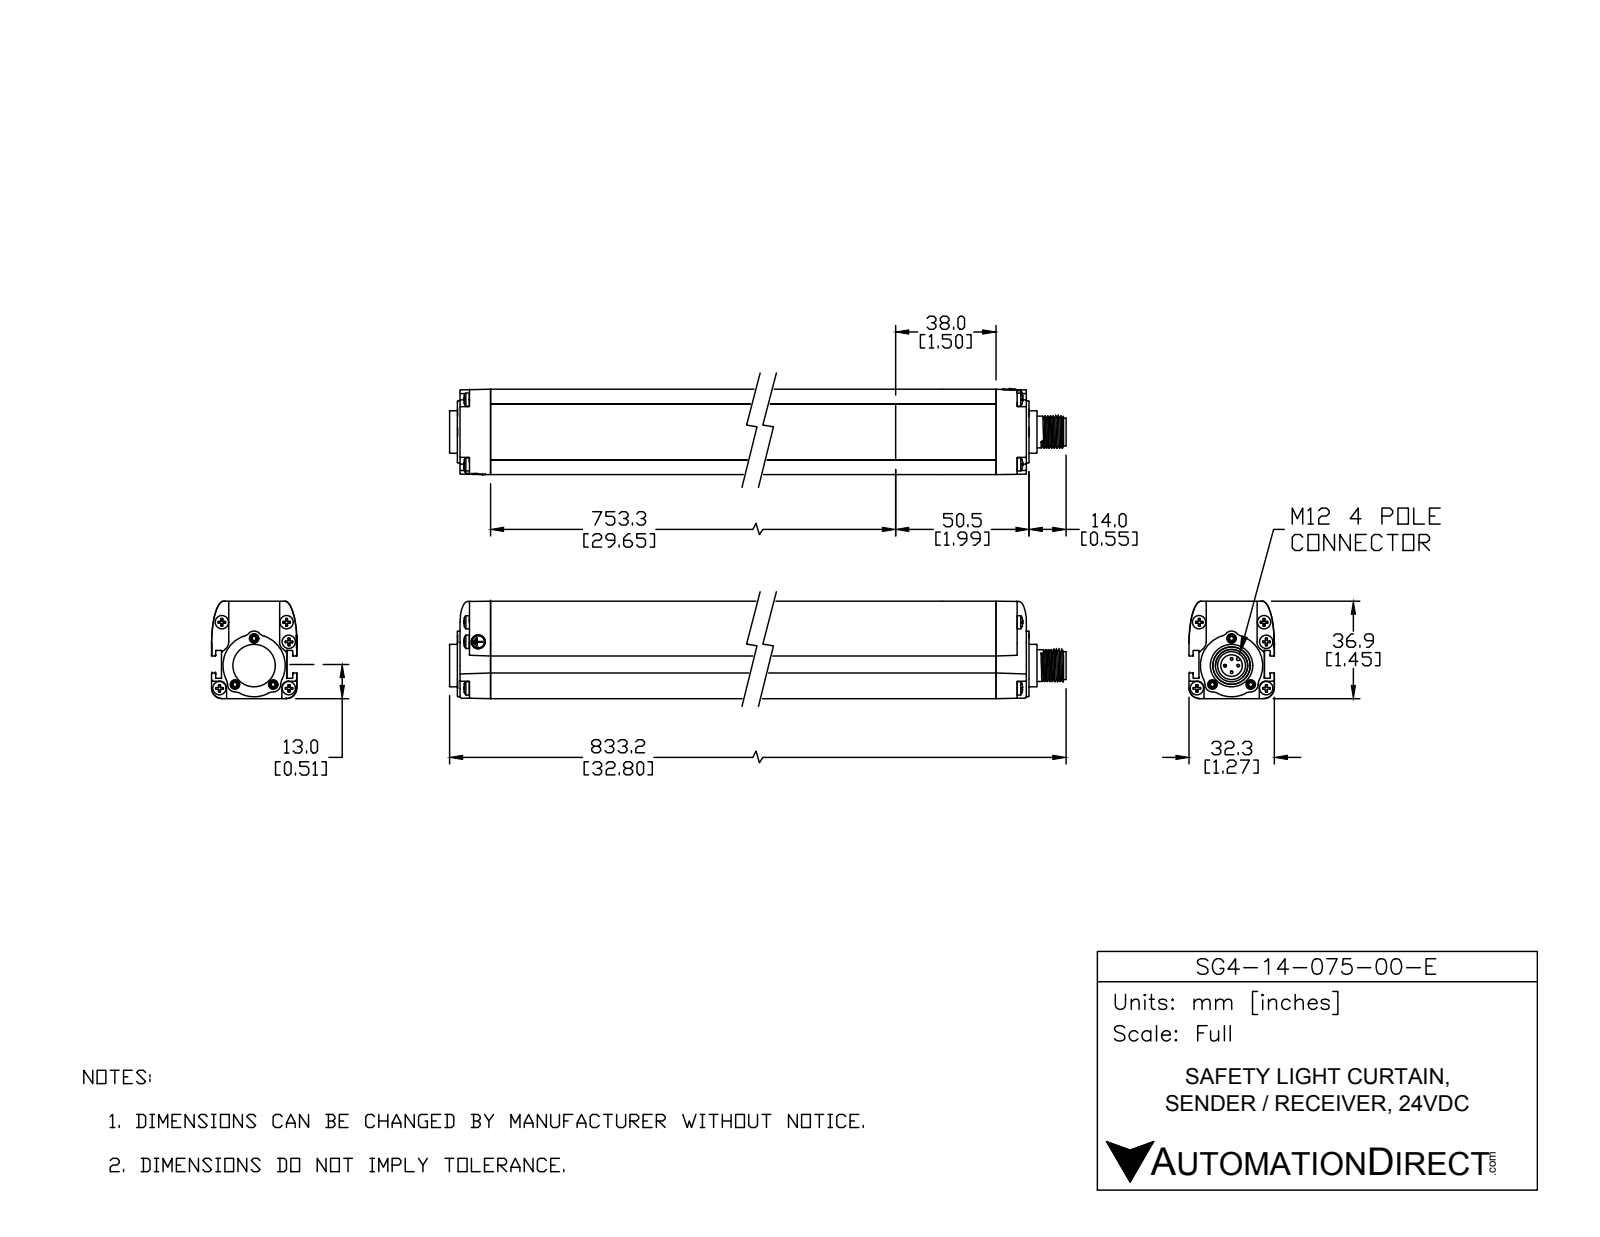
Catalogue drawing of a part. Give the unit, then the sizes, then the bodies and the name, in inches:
Units: inches
Overall size (bounding box): 32.805 × 2.48 × 2.055
Round holes (diameter × count): ⌀0.106 ×6, ⌀0.209 ×6, ⌀0.081 ×4, ⌀0.165 ×4, ⌀0.26 ×4, ⌀0.059 ×3, ⌀0.142 ×3, ⌀0.323 ×1, ⌀0.376 ×1, ⌀0.433 ×1, ⌀0.563 ×1
Round bosses / shafts (diameter × count): ⌀0.197 ×10, ⌀0.394 ×4, ⌀0.039 ×4, ⌀0.185 ×2, ⌀0.63 ×1, ⌀0.55 ×1, ⌀0.472 ×1, ⌀0.413 ×1
Partial cylindrical surfaces — rounded edges, fillets, slot ends (radius × count): R0.008 ×148, R0.004 ×120, R0.006 ×18, R0.106 ×18, R0.118 ×8, R0.197 ×7, R0.11 ×3, R0.016 ×2
Main face-to-face distances: 0.079, 1.272, 1.429, 0.15, 1.122, 1.35, 0.157, 0.972, 0.333, 0.118
Hole centre spacings: 0.569, 29.577, 0.402, 0.24, 0.293, 0.52, 0.541, 0.619
Volume: 52.24 in³ · Surface area: 325.6 in²
Bodies: 29 solids, 1674 faces (410 planar, 591 cylindrical, 673 other)
Part name (STEP PRODUCT): SG4-14-075-OO-E
STEP written by: SolidWorks 2017 (AUTOMOTIVE_DESIGN)
